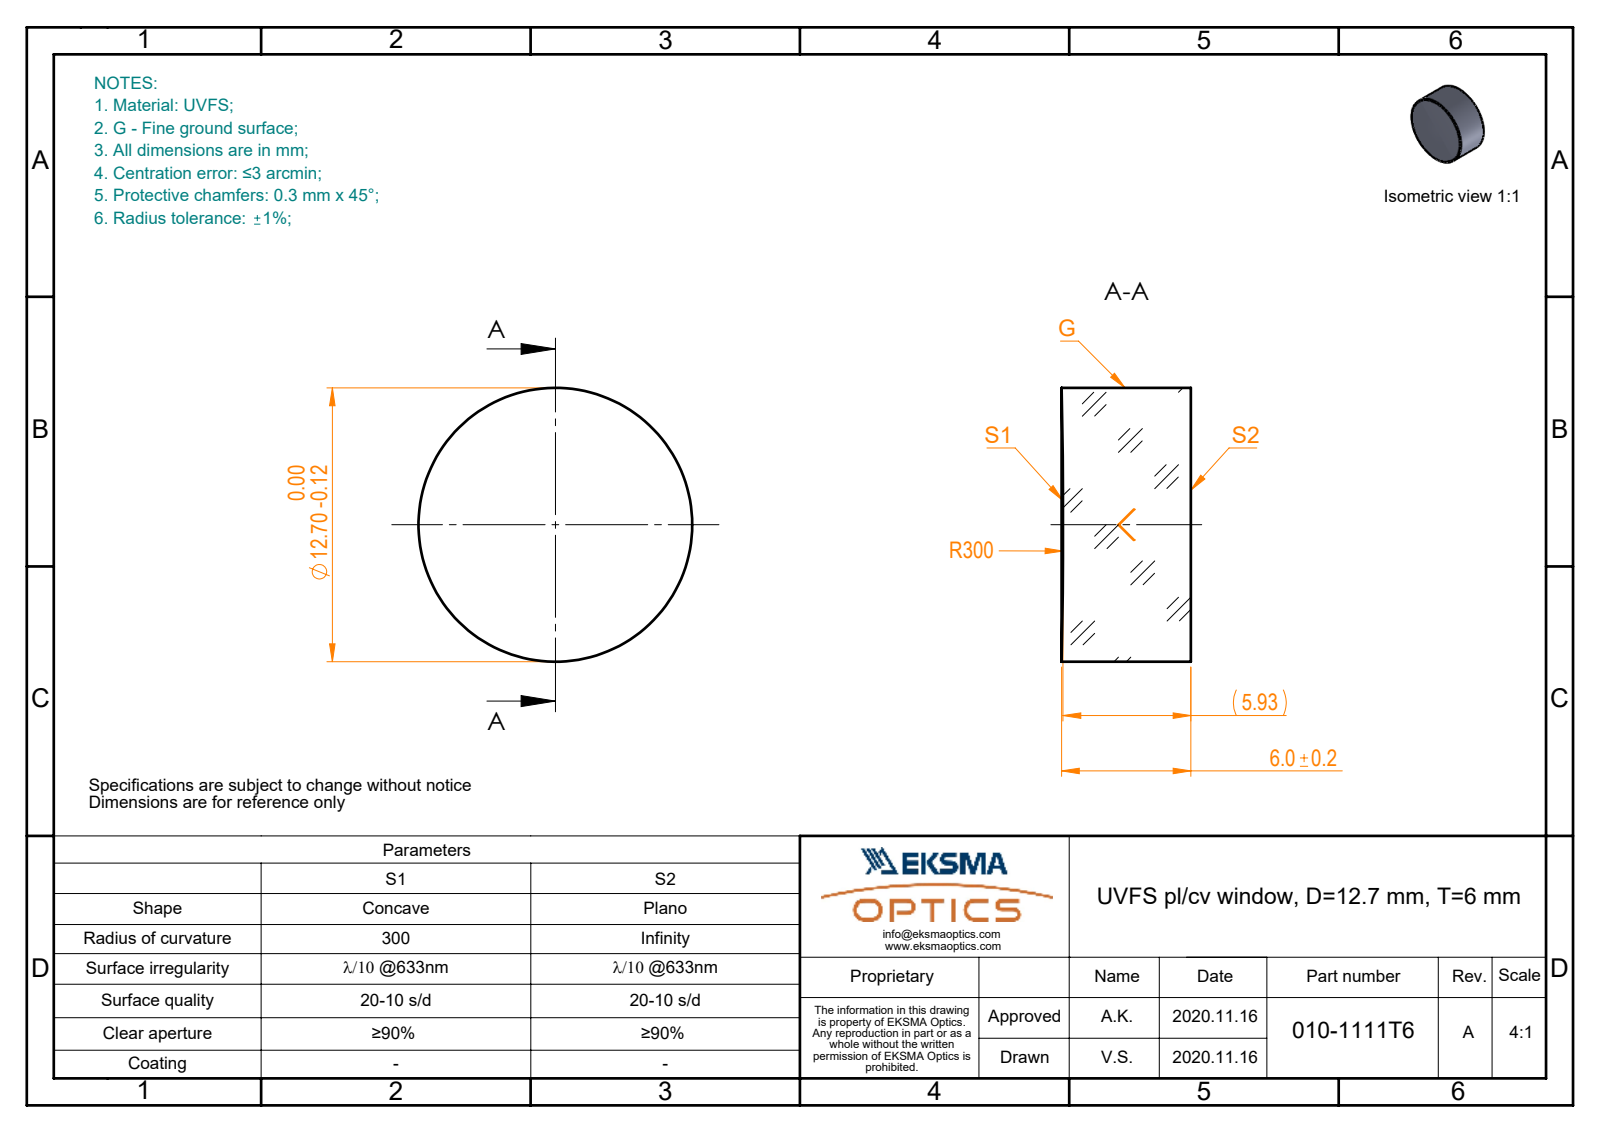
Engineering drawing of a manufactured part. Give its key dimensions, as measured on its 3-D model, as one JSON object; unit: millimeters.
{"part_name": "010-1111T6_UVFS_PCV_window", "step_written_by": "SolidWorks 2019 (CONFIG_CONTROL_DESIGN)", "units": "millimeters", "bodies": {"solids": 1, "faces": 5, "planar": 1, "cylindrical": 2, "other": 2}, "overall_size": [12.7, 12.7, 6], "volume_mm3": 756, "surface_area_mm2": 493, "round_bosses_or_shafts": [[12.7, 1]]}
